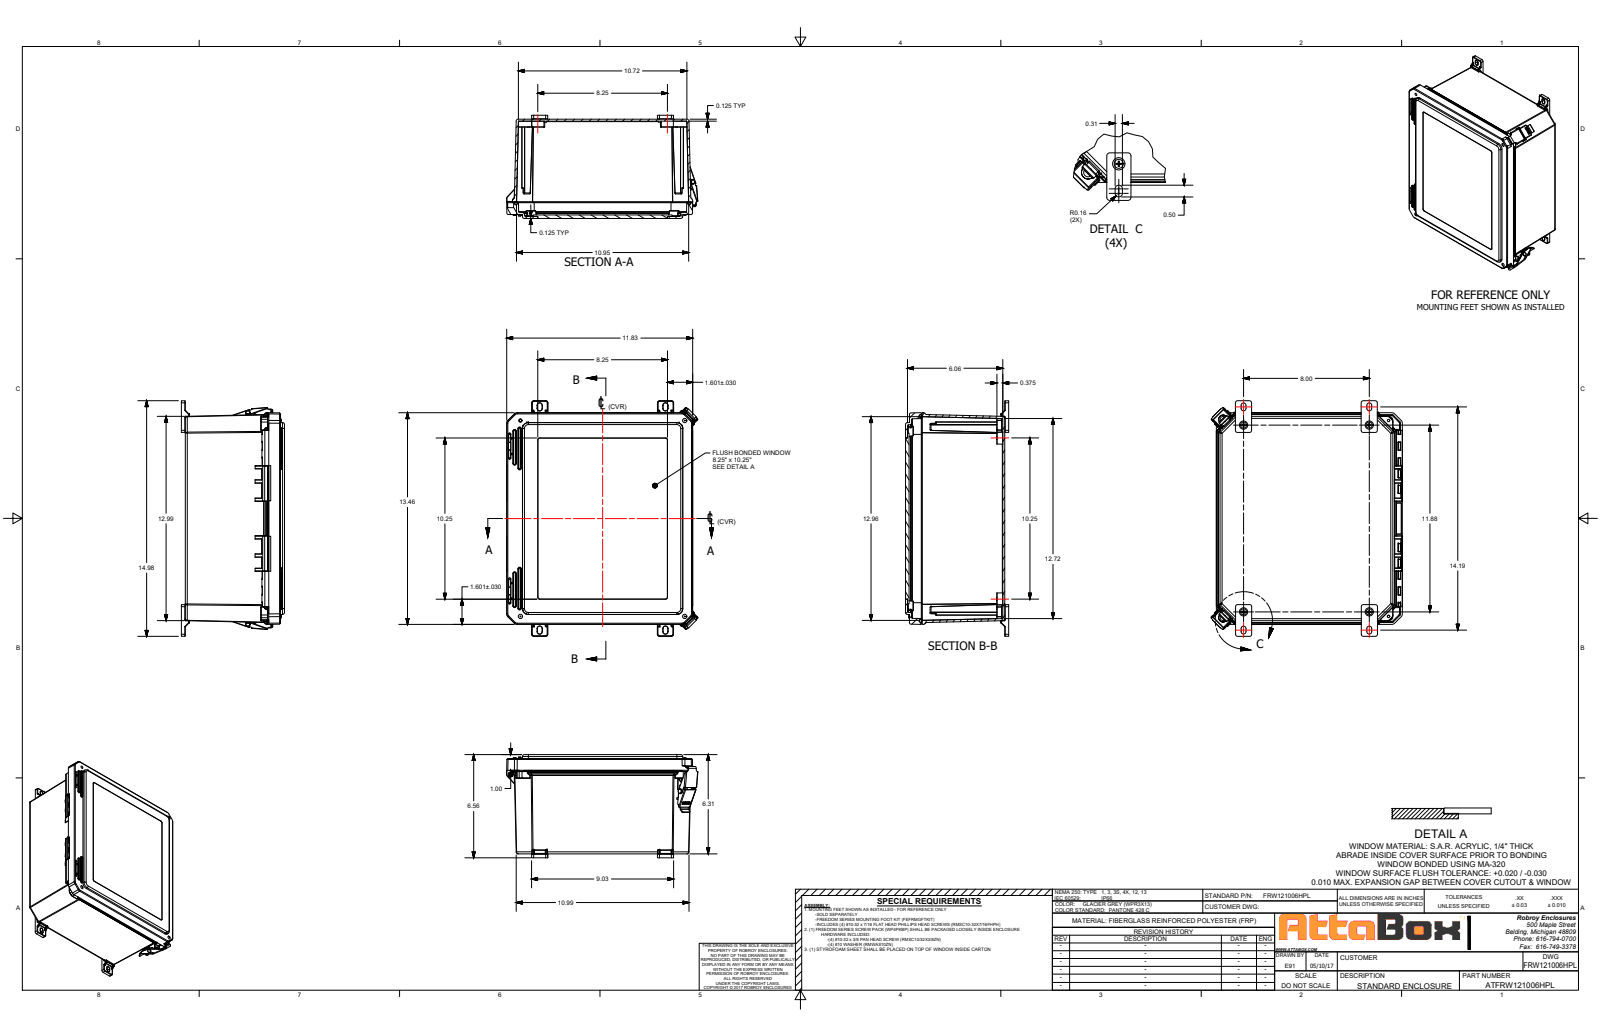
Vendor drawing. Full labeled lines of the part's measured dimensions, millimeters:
Part name (STEP PRODUCT): FRW121006HPL
STEP written by: SolidWorks 2021 (AUTOMOTIVE_DESIGN)
Units: millimetres
Bodies: 30 solids, 2420 faces (772 planar, 1040 cylindrical, 608 other)
Overall size (bounding box): 358.6 × 308.9 × 169.4
Volume: 1 691 000 mm³ · Surface area: 858 100 mm²
Round holes (diameter × count): ⌀3.4 ×8, ⌀3.9 ×8, ⌀4 ×8, ⌀3.4 ×4, ⌀3.8 ×4, ⌀4 ×4, ⌀6.4 ×4, ⌀6.4 ×4, ⌀3.5 ×3, ⌀5.6 ×2, ⌀5.8 ×2, ⌀8 ×2
Round bosses / shafts (diameter × count): ⌀6.9 ×8, ⌀22.1 ×4, ⌀7.6 ×4, ⌀6.7 ×4, ⌀5.3 ×4, ⌀3.4 ×3, ⌀11 ×1, ⌀11 ×1
Partial cylindrical surfaces — rounded edges, fillets, slot ends (radius × count): R0.3 ×174, R0.1 ×94, R0.8 ×71, R0.5 ×70, R1.5 ×36, R2.3 ×26, R3.2 ×26, R0.8 ×24
Main face-to-face distances: 3.2, 157, 160.2, 5.7, 151.4, 154.5, 3.6, 3.5, 3.6, 6.4
Hole centre spacings: 316.3, 316.4, 289.7, 299.9, 373.6, 310.6, 6.4, 239.2
